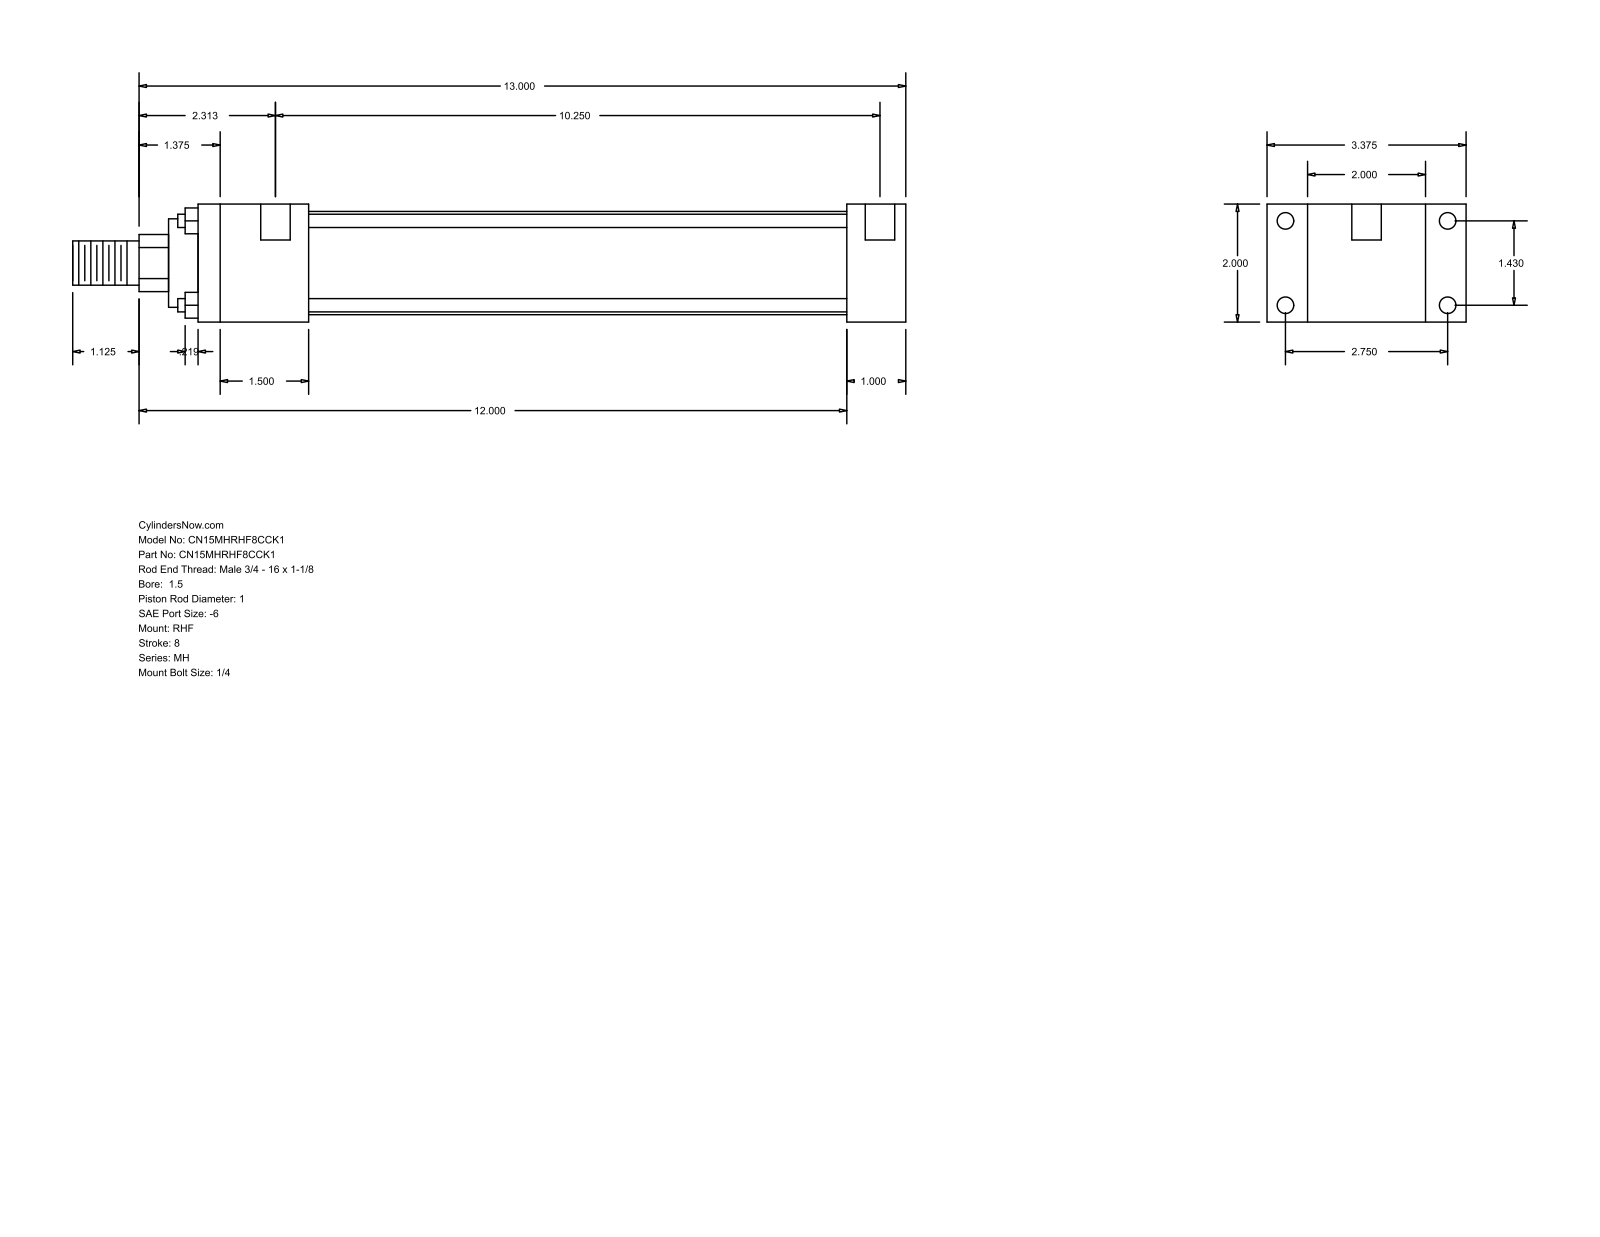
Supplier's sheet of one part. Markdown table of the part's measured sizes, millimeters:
| quantity | value |
| --- | --- |
| part name | MH_RHF__0150_1 |
| STEP written by | GSSL Pune (CONFIG_CONTROL_DESIGN) |
| units | millimeters |
| bodies | 0 solids, 88 faces (60 planar, 28 cylindrical, 0 other) |
| overall size | 358.77 × 85.72 × 50.8 |
| round holes (diameter × count) | 5.56 × 4, 7.14 × 4, 12.7 × 2 |
| round bosses / shafts (diameter × count) | 5.71 × 4, 44.45 × 1, 38.1 × 1, 25.4 × 1, 19.05 × 1 |
| partial cylindrical surfaces (radius × count) | 12.29 × 1 |
| main face-to-face distances | 50.8, 25.4, 17.46, 68.26, 85.72, 304.8, 279.4, 47.63, 231.77, 257.17 |
| hole center spacings | 36.32, 69.84, 78.72, 263.53, 3.18, 260.35 |
